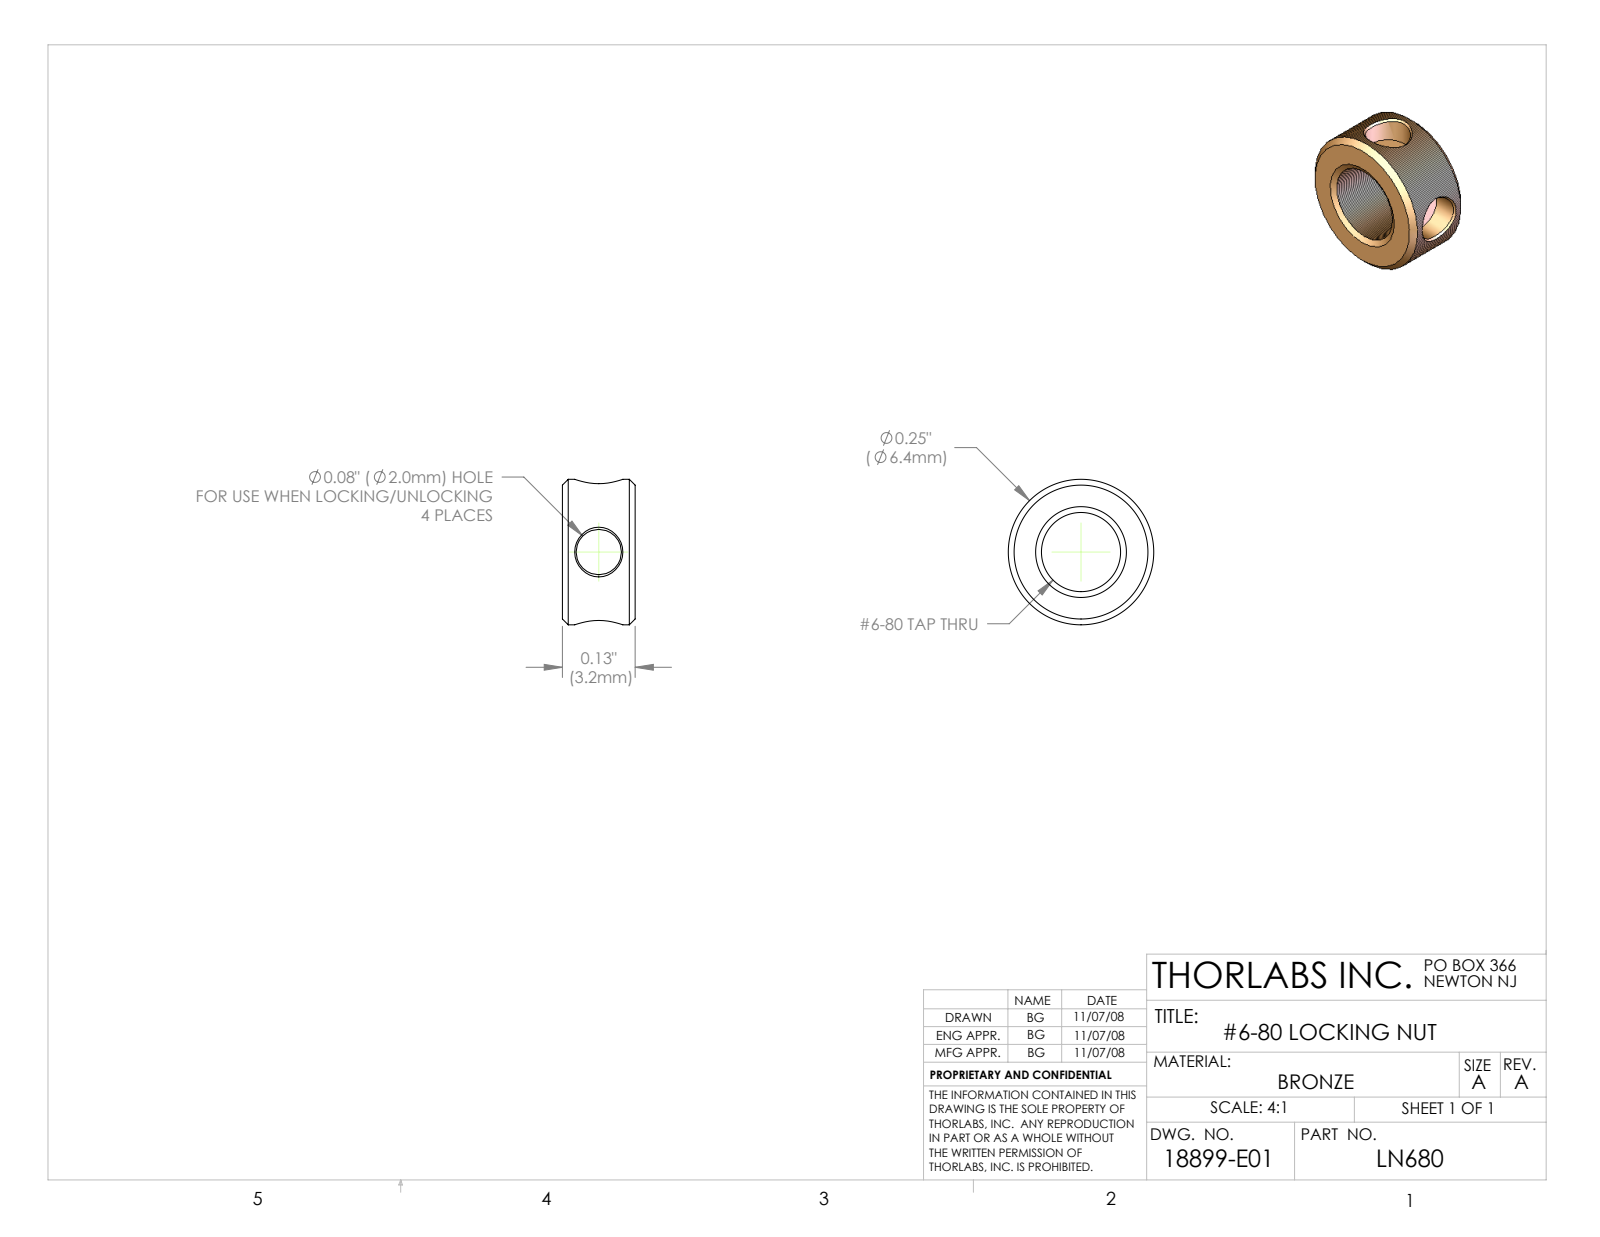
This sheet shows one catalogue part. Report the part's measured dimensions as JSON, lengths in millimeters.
{"part_name": "18899-E0W", "step_written_by": "SolidWorks 2007 (AUTOMOTIVE_DESIGN)", "units": "millimeters", "bodies": {"solids": 1, "faces": 34, "planar": 6, "cylindrical": 12, "other": 16}, "overall_size": [6.35, 6.35, 3.17], "volume_mm3": 55, "surface_area_mm2": 159, "round_holes": [[1.98, 2], [3.45, 1]], "round_bosses_or_shafts": [[6.35, 1]], "face_to_face_distances": [3.18, 4.06]}
